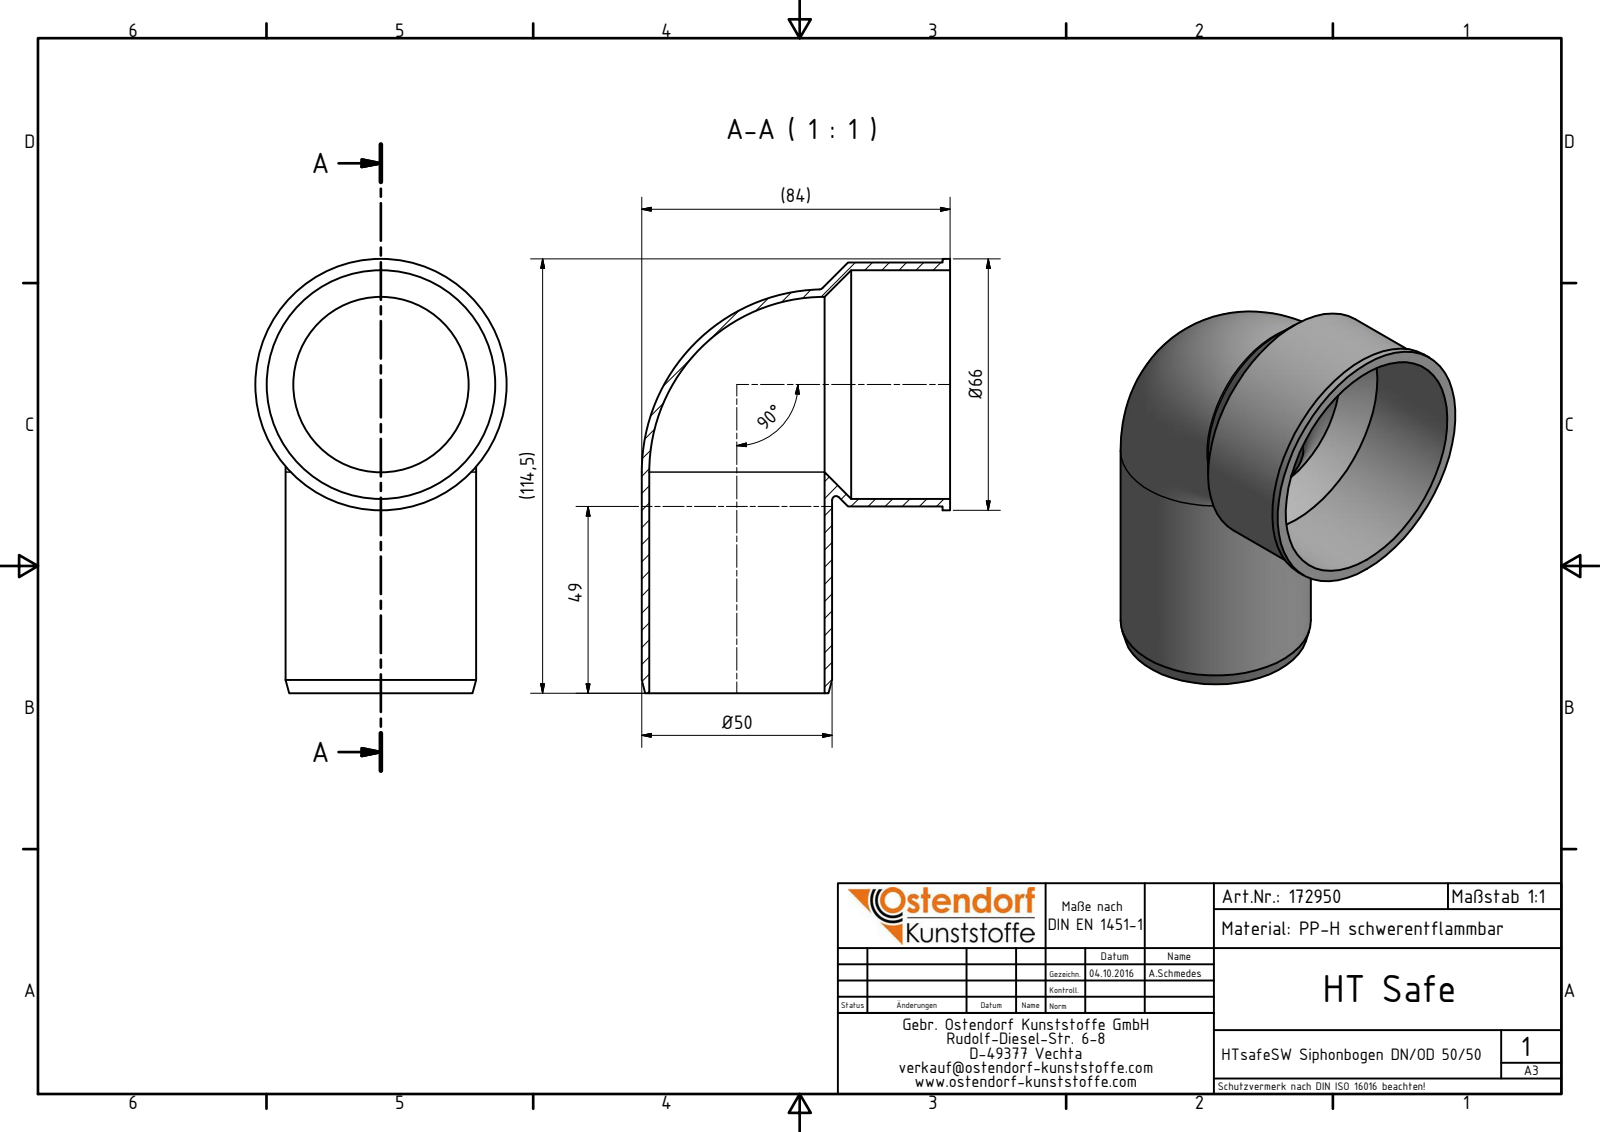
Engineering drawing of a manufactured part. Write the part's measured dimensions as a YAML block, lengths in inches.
part_name: "172950 HTsafeSW DN_OD 50_50"
step_written_by: "Autodesk Inventor 2016 (AUTOMOTIVE_DESIGN)"
units: inches
bodies: {solids: 1, faces: 15, planar: 3, cylindrical: 5, other: 7}
overall_size: [4.488, 3.189, 2.598]
volume: 2.42
surface_area: 66.38
round_holes:
  - {diameter: 1.811, count: 1}
  - {diameter: 2.362, count: 1}
round_bosses_or_shafts:
  - {diameter: 2.598, count: 1}
  - {diameter: 2.52, count: 1}
  - {diameter: 1.969, count: 1}
face_to_face_distances: [0.079]
